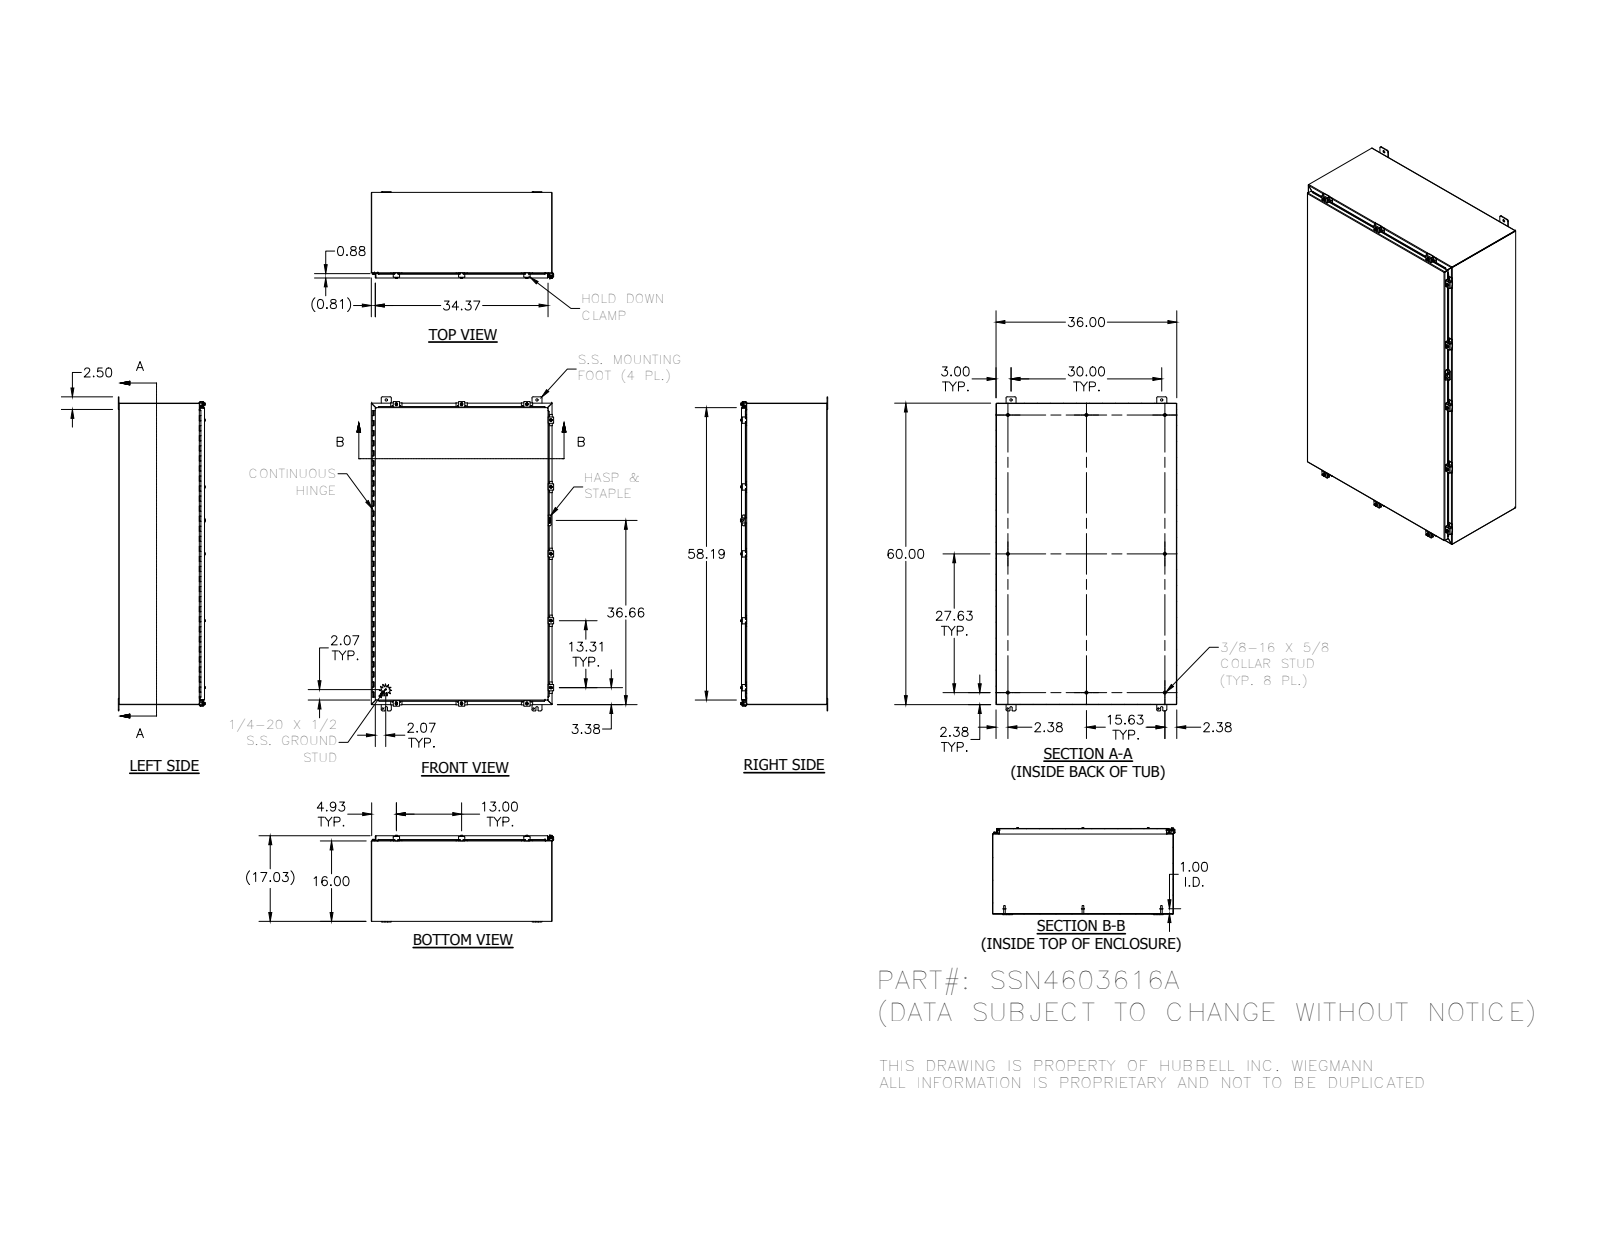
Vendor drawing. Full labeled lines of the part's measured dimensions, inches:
Part name (STEP PRODUCT): 32874-60L; 30819; 32874-60P; 34839 (+8 more)
STEP written by: SolidWorks 2014 (AUTOMOTIVE_DESIGN)
Units: inches
Bodies: 78 solids, 2976 faces (1222 planar, 1307 cylindrical, 447 other)
Overall size (bounding box): 62.5 × 36.311 × 17.355
Volume: 613.6 in³ · Surface area: 16 344 in²
Round holes (diameter × count): ⌀0.211 ×11, ⌀0.281 ×11, ⌀0.3 ×11, ⌀0.313 ×4, ⌀0.438 ×4, ⌀0.125 ×1, ⌀0.156 ×1, ⌀0.5 ×1
Round bosses / shafts (diameter × count): ⌀0.25 ×13, ⌀0.52 ×11, ⌀0.5 ×11, ⌀0.35 ×11, ⌀0.625 ×8, ⌀0.33 ×8, ⌀0.337 ×1, ⌀0.12 ×1
Partial cylindrical surfaces — rounded edges, fillets, slot ends (radius × count): R0.03 ×129, R0.125 ×43, R0.25 ×39, R0.141 ×22, R0.031 ×21, R0.105 ×21, R0.062 ×20, R0.1 ×16
Main face-to-face distances: 0.074, 16.959, 16.885, 17.033, 35.926, 59.926, 35.852, 36, 59.852, 60
Hole centre spacings: 1.593, 13, 30, 60, 61.018, 67.082, 13.313, 59.617
